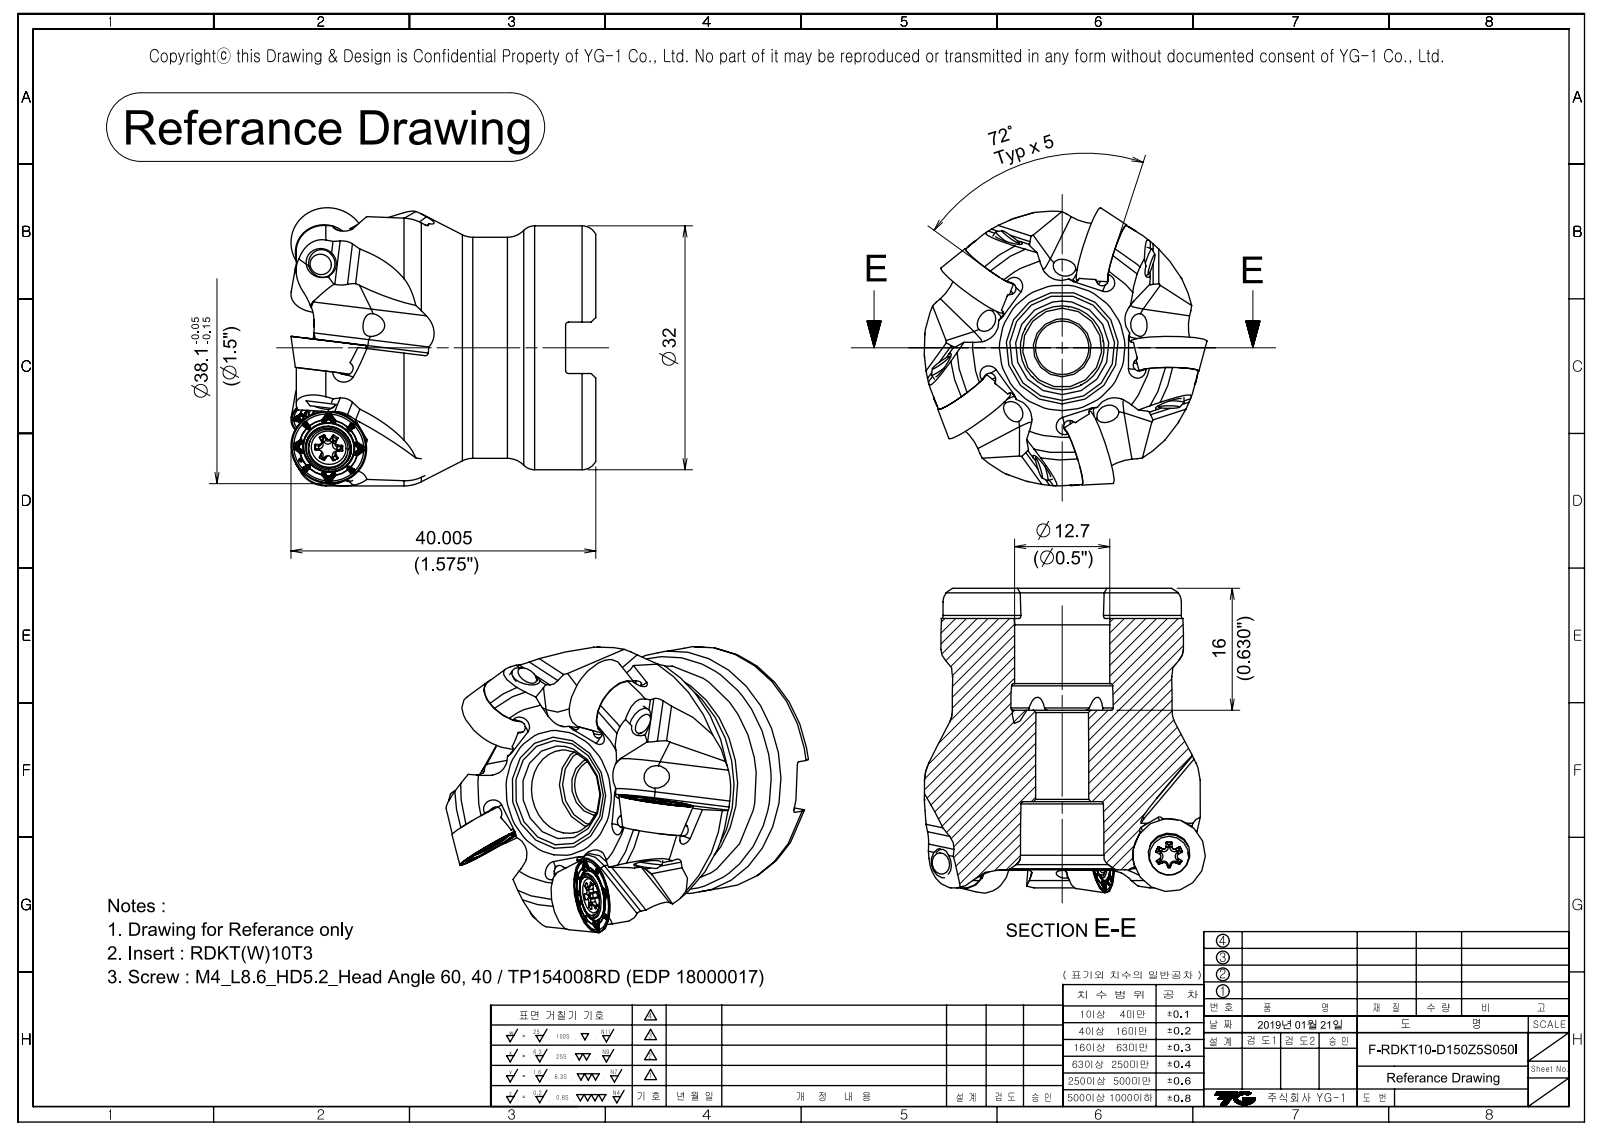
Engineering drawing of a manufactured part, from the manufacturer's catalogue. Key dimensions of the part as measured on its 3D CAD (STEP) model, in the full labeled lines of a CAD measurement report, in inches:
Part name (STEP PRODUCT): CUTTER-F-RDKT10-D150Z5S050I
STEP written by: SIEMENS PLM Software NX 10.0 (CONFIG_CONTROL_DESIGN)
Units: inches
Bodies: 11 solids, 2900 faces (197 planar, 296 cylindrical, 2407 other)
Overall size (bounding box): 1.575 × 1.463 × 1.437
Volume: 1.457 in³ · Surface area: 15.51 in²
Round holes (diameter × count): ⌀0.118 ×5, ⌀0.138 ×5, ⌀0.173 ×5, ⌀0.276 ×1, ⌀0.433 ×1, ⌀0.5 ×1, ⌀0.531 ×1
Round bosses / shafts (diameter × count): ⌀0.205 ×5, ⌀0.157 ×5, ⌀0.146 ×5, ⌀1.26 ×1, ⌀1.142 ×1
Partial cylindrical surfaces — rounded edges, fillets, slot ends (radius × count): R0.012 ×90, R0.004 ×60, R0.059 ×20, R0.016 ×17, R0.118 ×10, R0.098 ×5, R0.315 ×5, R1.378 ×5
Main face-to-face distances: 0.142, 0.156, 0.266, 0.474, 0.63, 0.142, 0.824, 1.298, 1.454, 0.352
